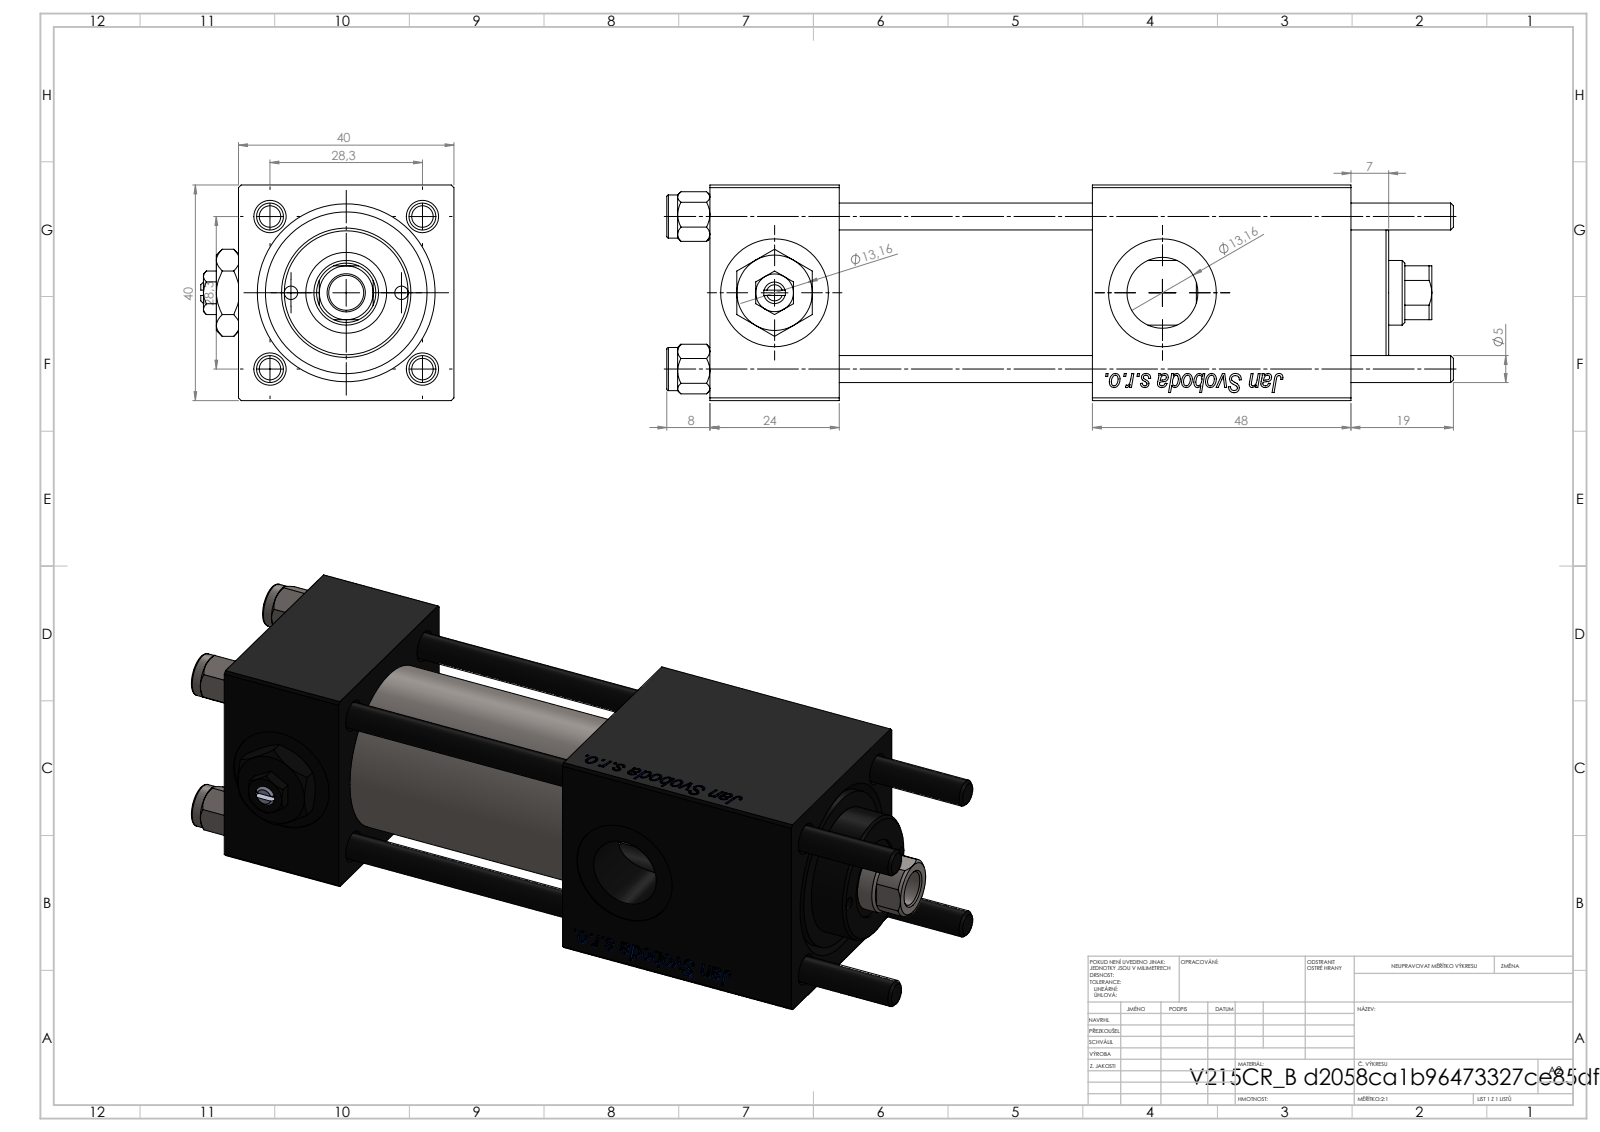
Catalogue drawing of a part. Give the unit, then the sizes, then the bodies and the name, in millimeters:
Units: millimetres
Overall size (bounding box): 146 × 47 × 40
Round holes (diameter × count): ⌀5 ×4, ⌀20 ×3, ⌀2.5 ×2, ⌀7 ×2, ⌀13.16 ×2, ⌀6.5 ×1, ⌀12 ×1, ⌀15 ×1, ⌀25 ×1, ⌀30 ×1
Round bosses / shafts (diameter × count): ⌀8 ×4, ⌀31 ×1, ⌀24 ×1
Partial cylindrical surfaces — rounded edges, fillets, slot ends (radius × count): R5.5 ×1
Main face-to-face distances: 40, 24, 90.3, 66.3, 119, 47, 71, 19.3, 95, 48
Hole centre spacings: 14.68, 20.01, 28.21, 28.3, 10.25, 40.02, 20.5, 72
Volume: 144 013 mm³ · Surface area: 59 832 mm²
Bodies: 12 solids, 1214 faces (454 planar, 90 cylindrical, 670 other)
Part name (STEP PRODUCT): V215CR_B-1; Zatka_pro_OIL_PORT; V215CR_VCP_B; V215_VC_A (+2 more)
STEP written by: SolidWorks 2019 (CONFIG_CONTROL_DESIGN)
